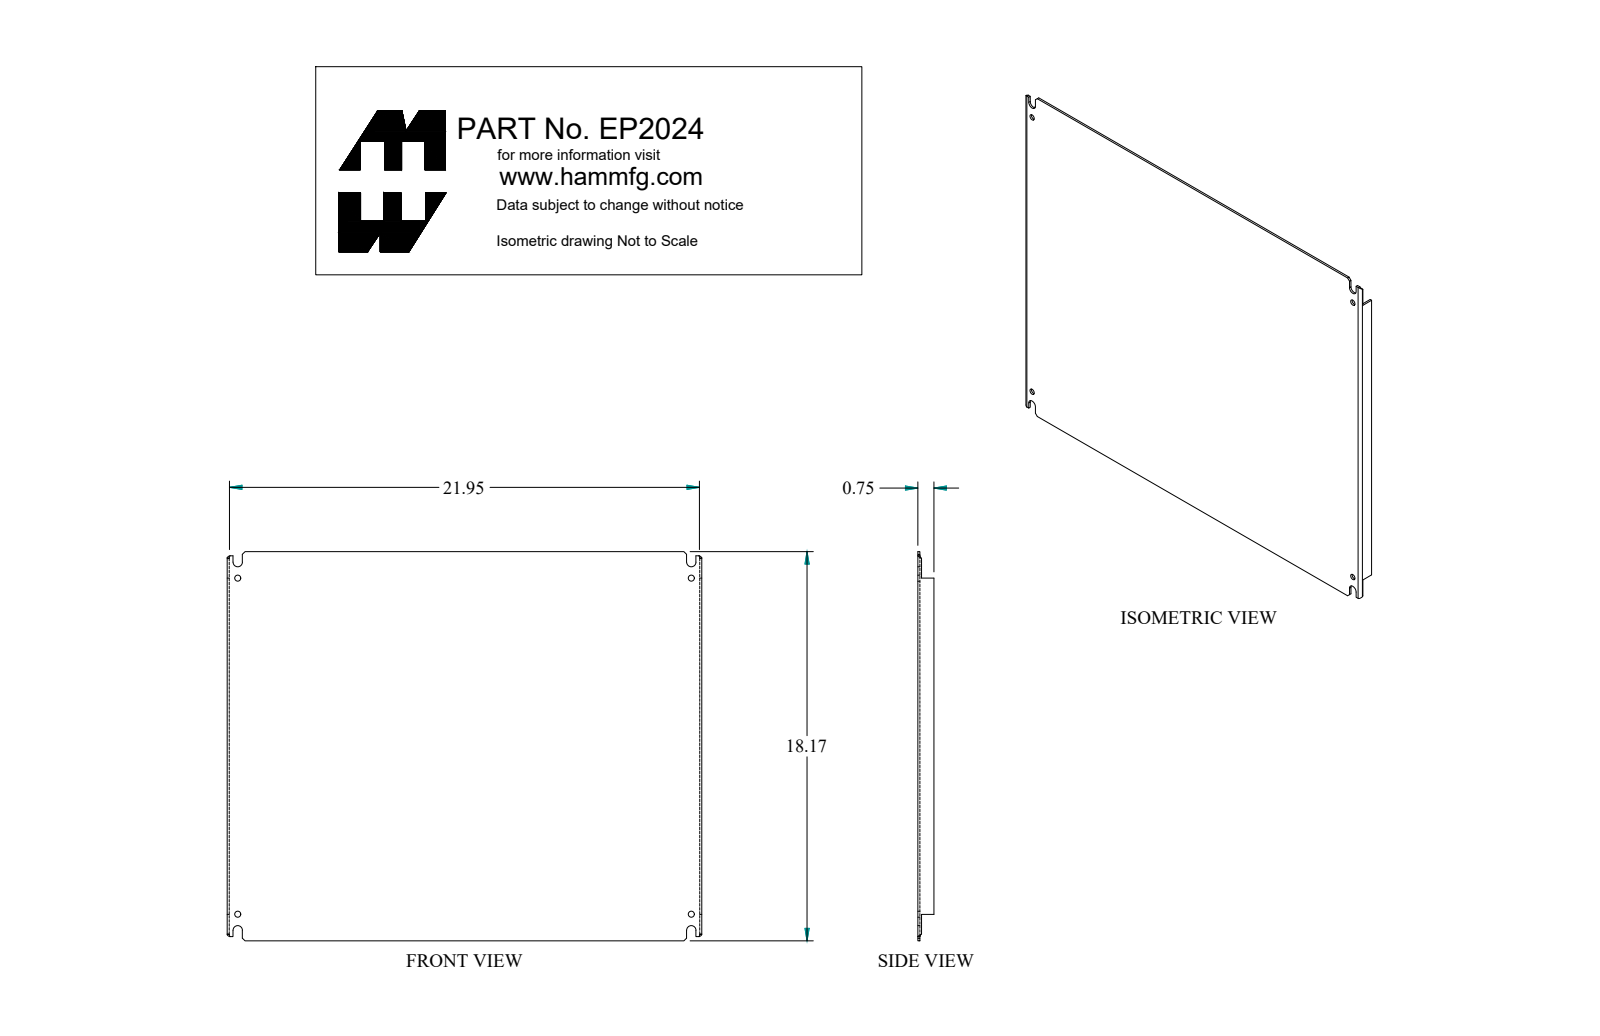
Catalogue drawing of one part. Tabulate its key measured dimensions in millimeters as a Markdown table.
| quantity | value |
| --- | --- |
| part name | EP2024 |
| STEP written by | SolidWorks 2018 (AUTOMOTIVE_DESIGN) |
| units | millimeters |
| bodies | 1 solid, 84 faces (50 planar, 26 cylindrical, 8 other) |
| overall size | 563.1 × 461.5 × 19.1 |
| volume | 654 700 mm³ |
| surface area | 548 100 mm² |
| round holes (diameter × count) | 7.1 × 4 |
| partial cylindrical surfaces (radius × count) | 5.6 × 4, 1.2 × 2, 1.6 × 2, 3.6 × 2 |
| main face-to-face distances | 2.4, 560.7, 558.3, 563.1, 19.1, 16.6, 461.5, 4.3, 1.9, 14.7 |
| hole center spacings | 398.5, 538.2, 669.6 |
